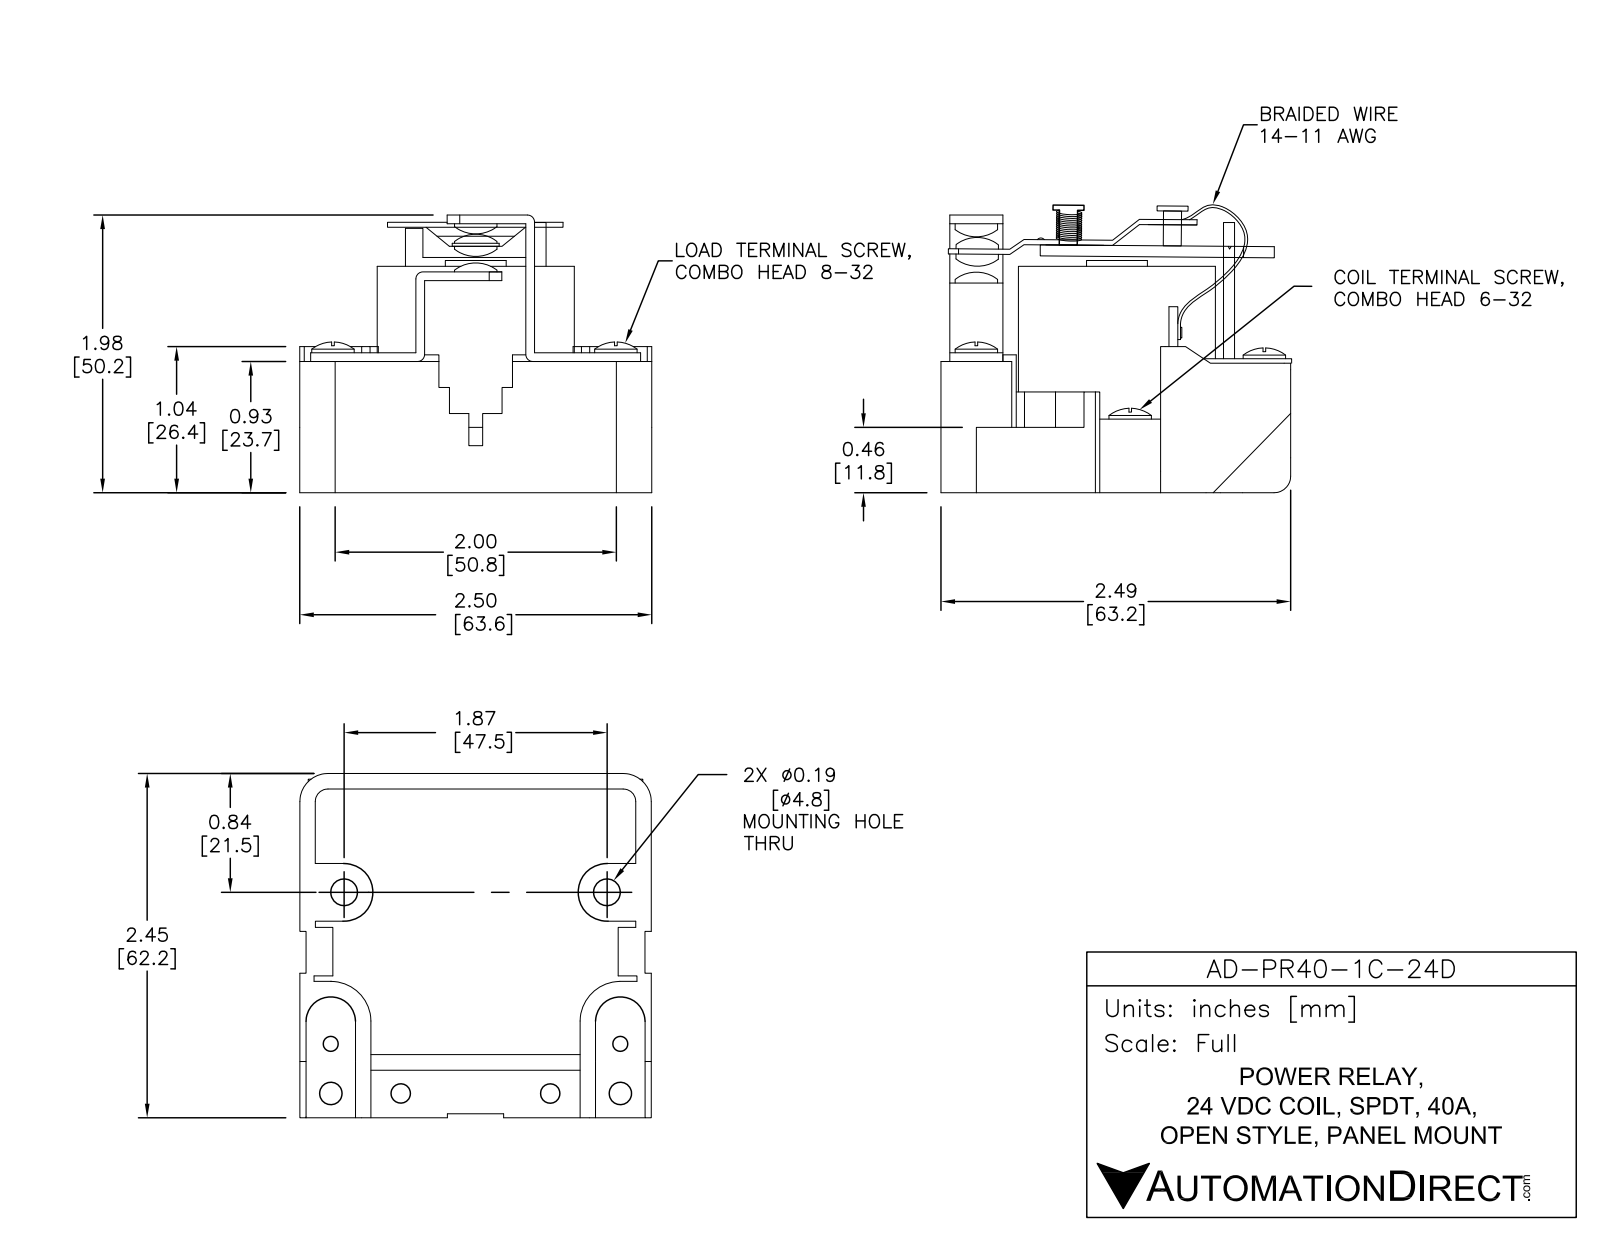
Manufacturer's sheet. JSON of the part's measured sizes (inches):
{"part_name": "AD-PR40-1C-24D", "step_written_by": "SolidWorks 2013 (AUTOMOTIVE_DESIGN)", "units": "inches", "bodies": {"solids": 34, "faces": 632, "planar": 415, "cylindrical": 128, "other": 89}, "overall_size": [2.557, 2.524, 2.03], "volume_in3": 5.555, "surface_area_in2": 51.83, "round_holes": [[0.197, 4], [0.098, 2], [0.131, 2], [0.394, 2], [1.181, 1]], "round_bosses_or_shafts": [[0.305, 3], [0.27, 2], [0.208, 2], [1.398, 1], [0.709, 1], [0.394, 1], [0.256, 1], [0.217, 1]], "partial_cylinders_radius": [[0.03, 10], [0.118, 6], [0.015, 4], [0.039, 4], [0.058, 4], [0.059, 4], [0.079, 3], [0.02, 2]], "face_to_face_distances": [0.472, 0.079, 0.394, 2.52, 1.289, 0.069, 0.039, 0.059, 1.211, 0.256], "hole_center_spacings": [0.394, 1.031, 1.083, 1.178, 1.439, 1.477, 1.939, 1.978]}
